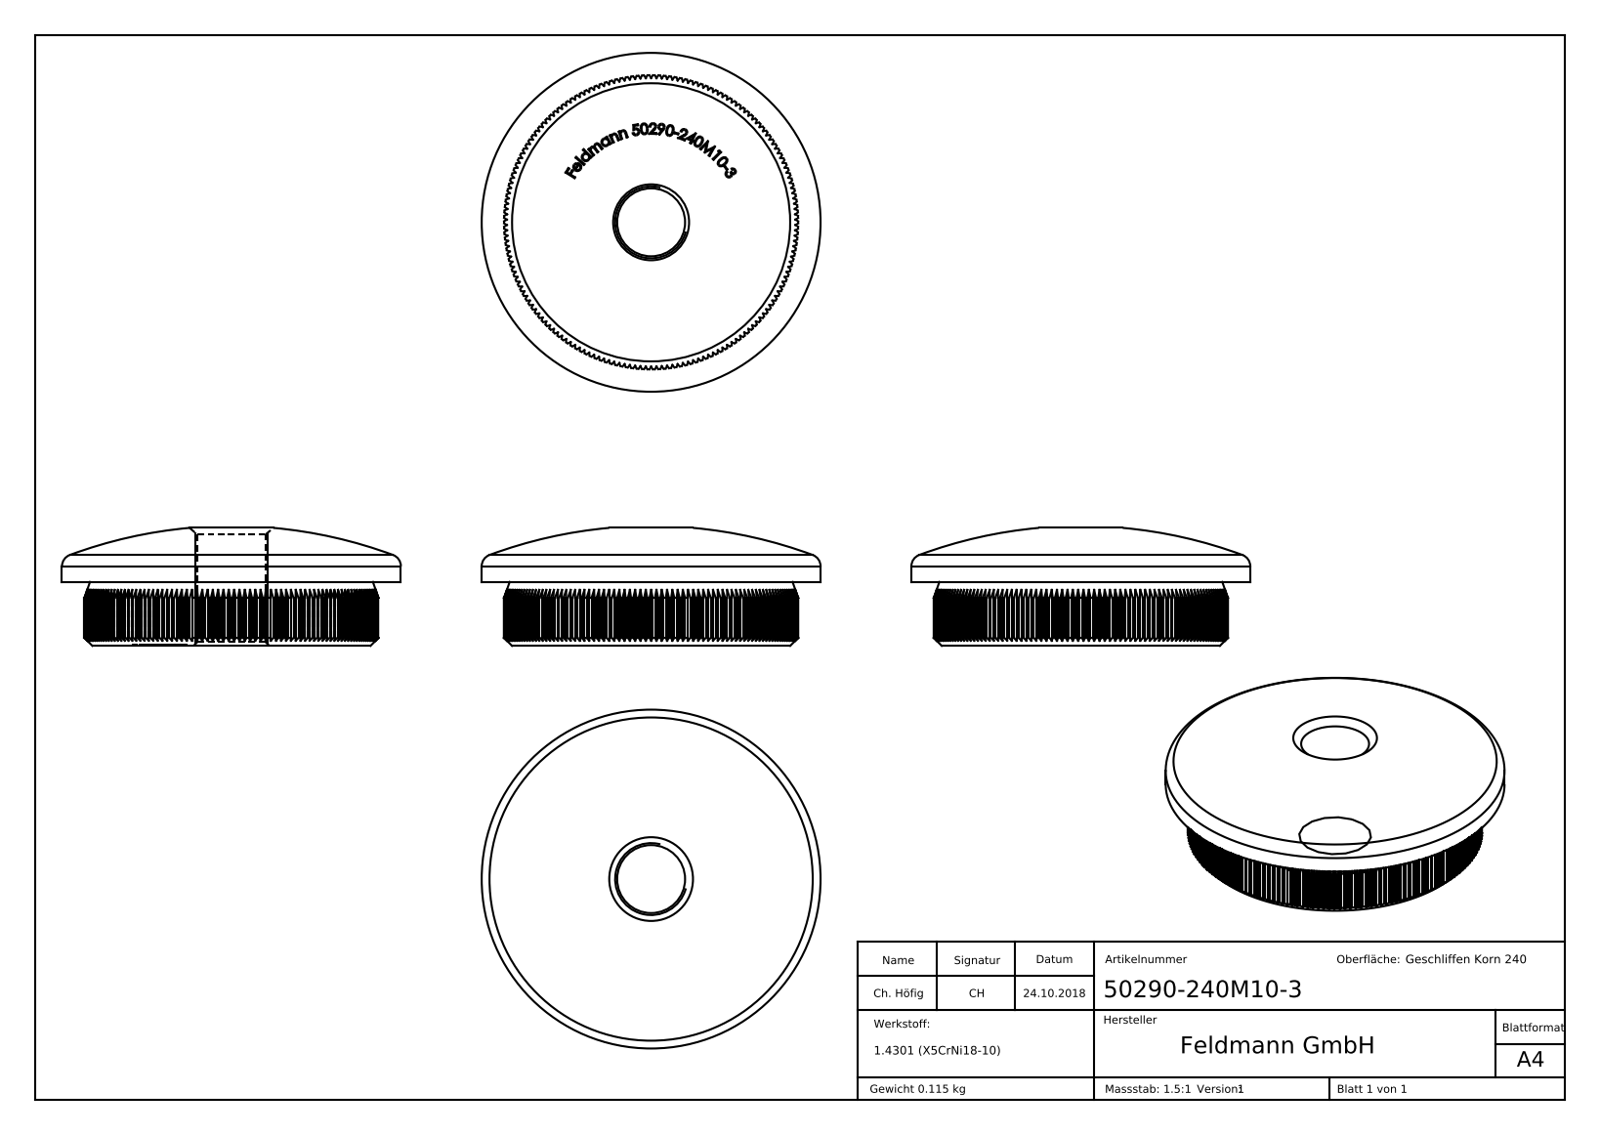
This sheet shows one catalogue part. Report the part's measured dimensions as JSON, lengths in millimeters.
{"part_name": "50290-240M10-3", "step_written_by": "SolidWorks 2015 (CONFIG_CONTROL_DESIGN)", "units": "millimeters", "bodies": {"solids": 1, "faces": 753, "planar": 472, "cylindrical": 174, "other": 107}, "overall_size": [42.4, 42.4, 14.76], "volume_mm3": 14510, "surface_area_mm2": 4834, "round_holes": [[8.5, 1]], "round_bosses_or_shafts": [[42.4, 1]], "partial_cylinders_radius": [[18.4, 1]], "face_to_face_distances": [8, 18.06, 18.04, 18.08, 7.9, 0.66, 0.54, 0.67, 0.79, 0.72]}
